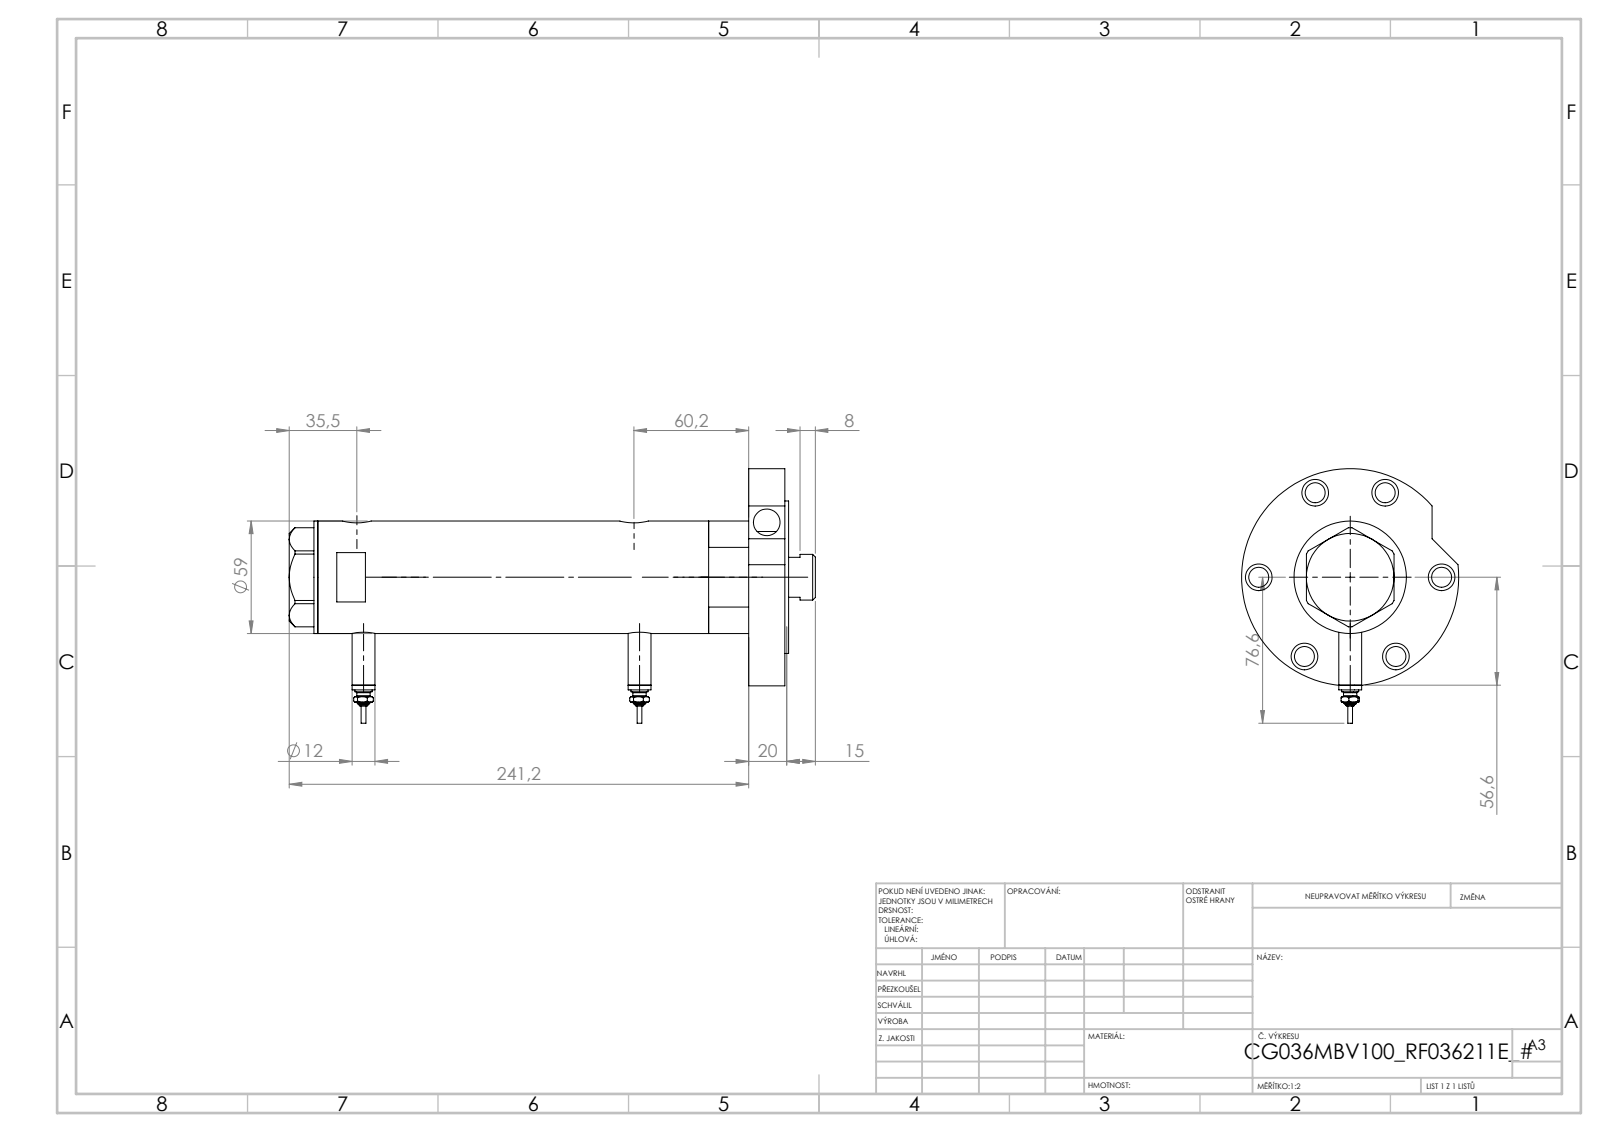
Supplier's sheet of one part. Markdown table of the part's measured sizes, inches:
| quantity | value |
| --- | --- |
| part name | V270CG_VC; V270CG_BACK; V270CG_RF211E; V270CG_MIDDLE (+2 more) |
| STEP written by | SolidWorks 2019 (CONFIG_CONTROL_DESIGN) |
| units | inches |
| bodies | 7 solids, 256 faces (90 planar, 102 cylindrical, 64 other) |
| overall size | 10.874 × 5.26 × 4.488 |
| volume | 47.11 in³ |
| surface area | 249.9 in² |
| round holes (diameter × count) | 0.551 × 7, 0.413 × 6, 0.383 × 2, 0.492 × 2, 0.591 × 2, 0.335 × 1, 0.984 × 1, 1.043 × 1, 1.417 × 1, 1.575 × 1, 1.89 × 1, 2.047 × 1 |
| round bosses / shafts (diameter × count) | 0.472 × 2, 0.354 × 2, 0.276 × 2, 0.177 × 2, 0.098 × 2, 4.488 × 1, 3.15 × 1, 2.323 × 1 |
| main face-to-face distances | 0.079, 0.748, 0.827, 9.732, 8.906, 9.654, 6.583, 2.323, 3.071, 3.15 |
| hole center spacings | 1.89, 2.1, 3.143, 3.273, 3.39, 3.772, 0.114, 0.138 |
